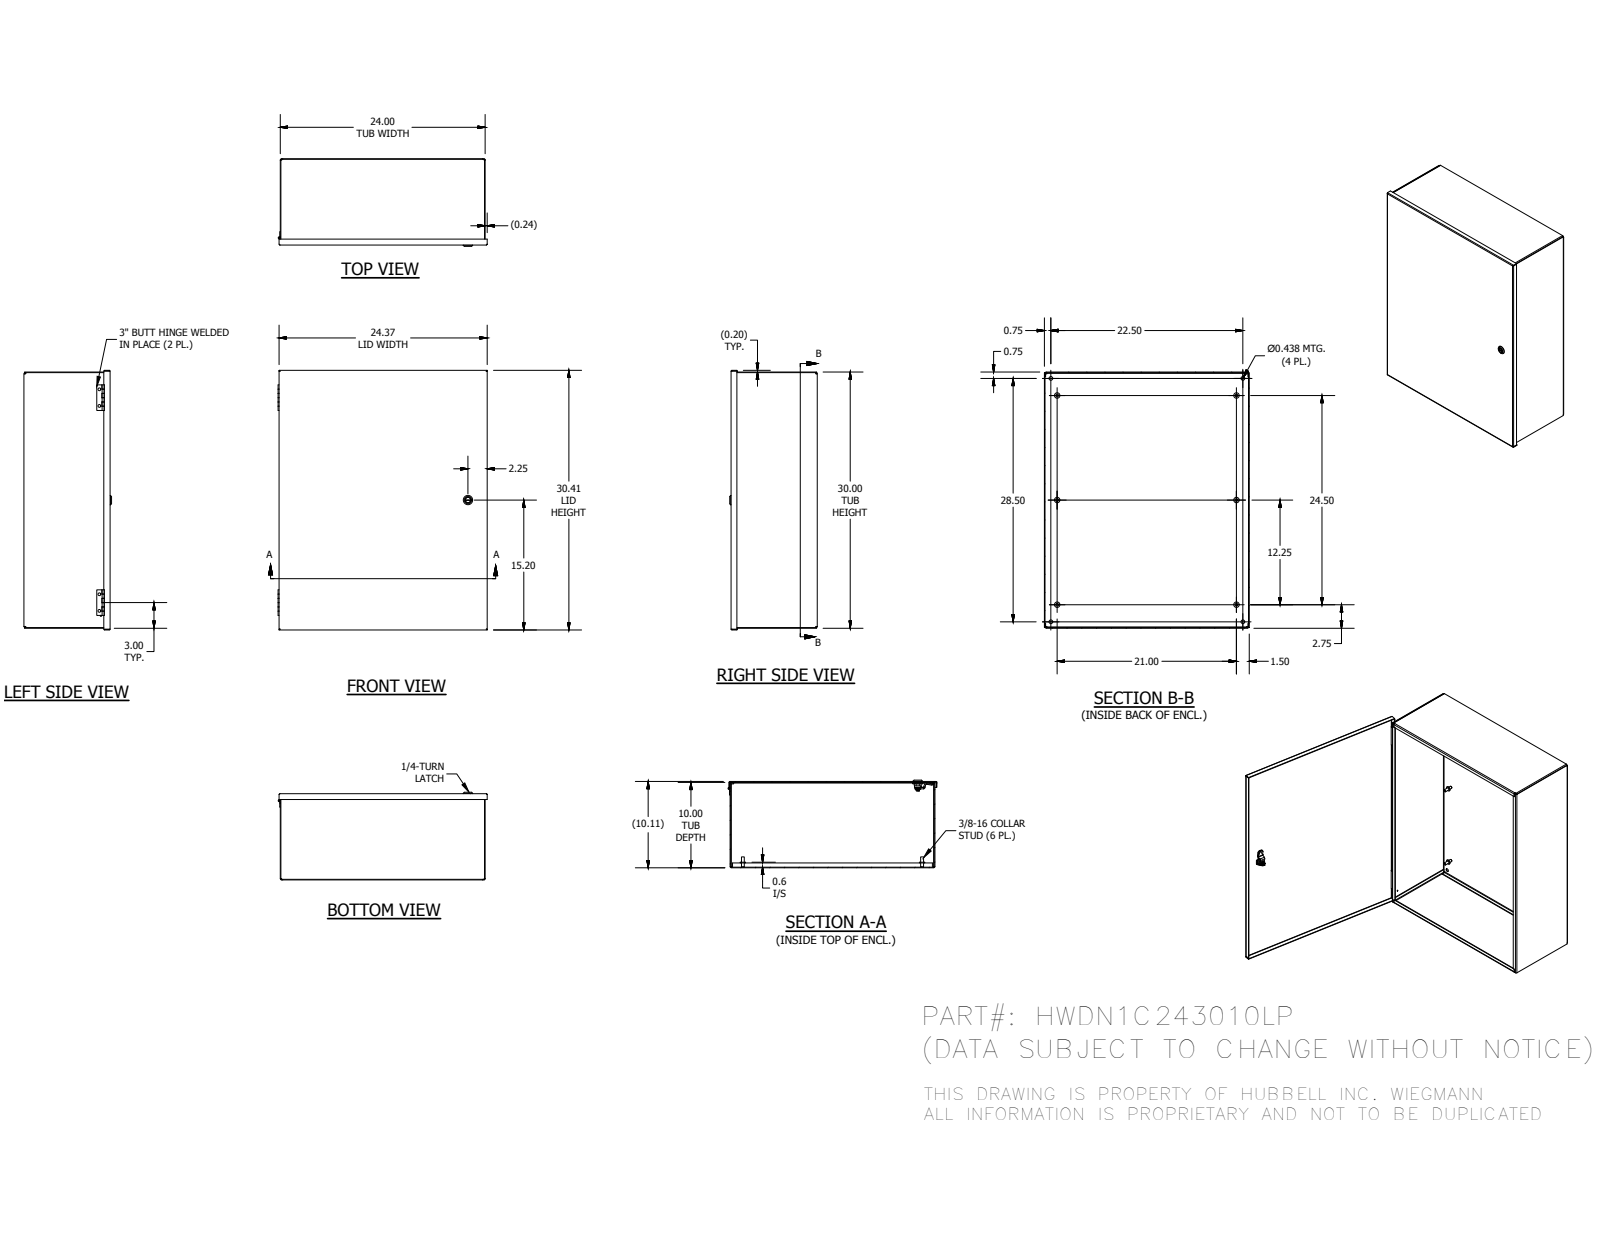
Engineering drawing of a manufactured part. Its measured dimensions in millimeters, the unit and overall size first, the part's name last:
Units: millimetres
Overall size (bounding box): 772.32 × 622.01 × 279.72
Round holes (diameter × count): ⌀7.95 ×4, ⌀11.11 ×4, ⌀3.05 ×1, ⌀3.3 ×1, ⌀5 ×1, ⌀8 ×1, ⌀10 ×1, ⌀10.2 ×1, ⌀16.1 ×1, ⌀20.38 ×1
Round bosses / shafts (diameter × count): ⌀15.88 ×6, ⌀8.38 ×6, ⌀28 ×1, ⌀27 ×1, ⌀23 ×1, ⌀19.8 ×1, ⌀15.8 ×1, ⌀15.2 ×1
Partial cylindrical surfaces — rounded edges, fillets, slot ends (radius × count): R0.3 ×30, R3.47 ×12, R1.59 ×11, R0.5 ×10, R0.79 ×4, R2.67 ×4, R4 ×4, R0.4 ×3
Main face-to-face distances: 1.88, 273.84, 271.96, 275.72, 607.72, 760.12, 605.84, 609.6, 758.24, 762
Hole centre spacings: 49.28, 363.37, 571.5, 609.6, 649.63, 723.9, 922.3, 15.51
Volume: 3 374 000 mm³ · Surface area: 3 606 000 mm²
Bodies: 23 solids, 733 faces (445 planar, 218 cylindrical, 70 other)
Part name (STEP PRODUCT): N1C243010LPBLR; N1C2410LPTB; N1C2430LPLID; 1000-101-GPF_GPD (+8 more)
STEP written by: Autodesk Inventor 2016 (AUTOMOTIVE_DESIGN)
